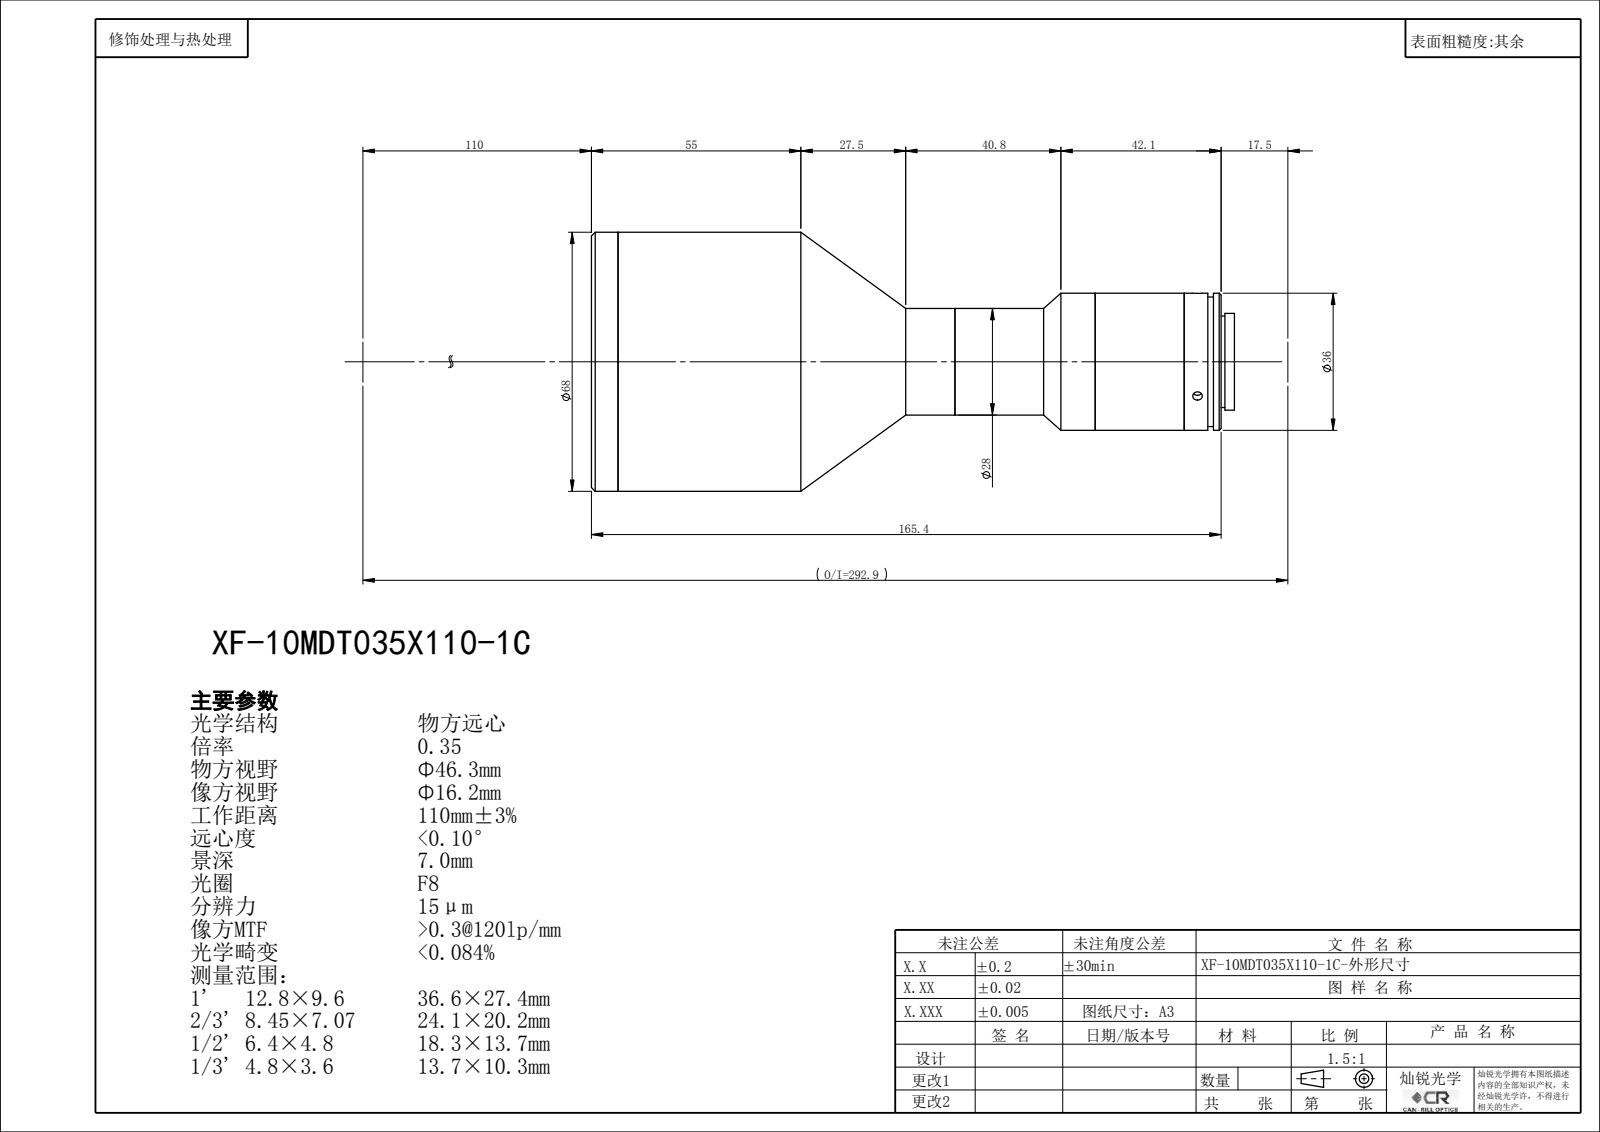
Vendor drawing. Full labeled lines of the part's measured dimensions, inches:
Part name (STEP PRODUCT): XF-5MDT035X110-1C
STEP written by: SolidWorks 2014 (CONFIG_CONTROL_DESIGN)
Units: inches
Bodies: 0 solids, 76 faces (22 planar, 42 cylindrical, 12 other)
Overall size (bounding box): 6.648 × 2.677 × 2.677
Round holes (diameter × count): ⌀0.098 ×3, ⌀0.843 ×1, ⌀0.945 ×1, ⌀2.126 ×1, ⌀2.283 ×1, ⌀2.48 ×1
Round bosses / shafts (diameter × count): ⌀2.677 ×1, ⌀1.417 ×1, ⌀1.339 ×1, ⌀1.102 ×1, ⌀1 ×1
Main face-to-face distances: 0.276, 6.128, 5.853, 6.51, 6.235, 0.382, 0.126, 0.15, 6.002, 6.384
